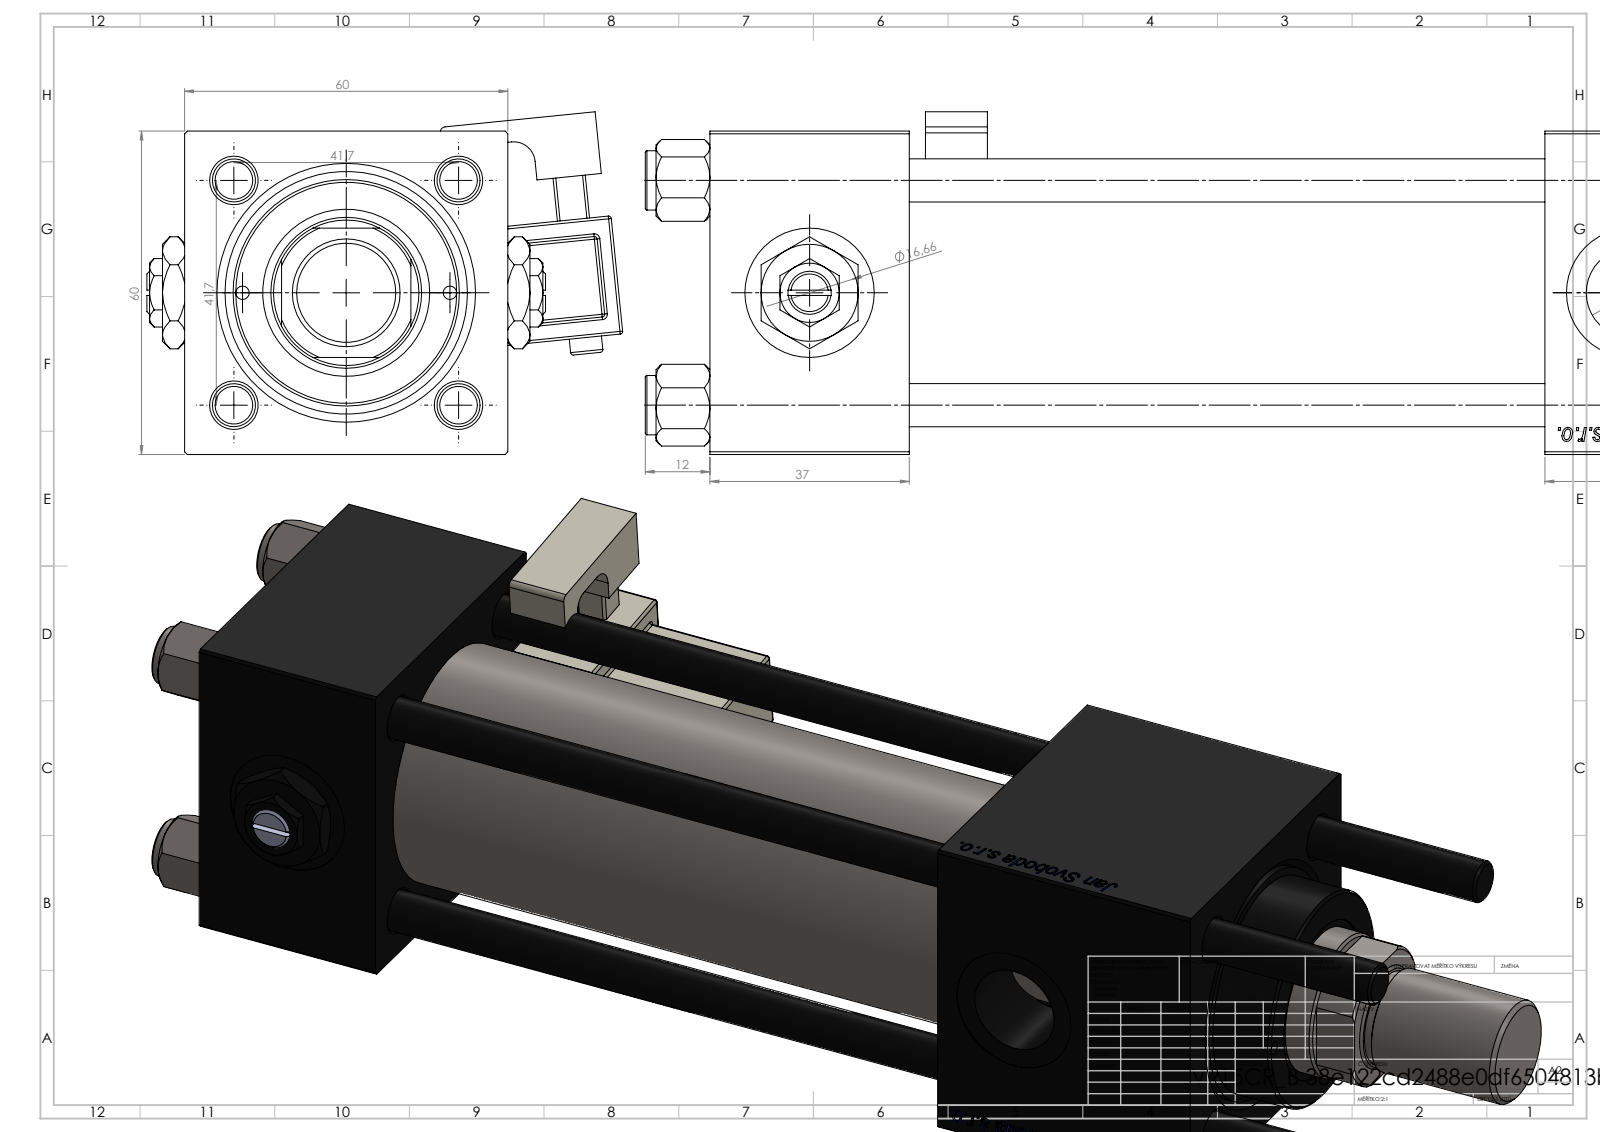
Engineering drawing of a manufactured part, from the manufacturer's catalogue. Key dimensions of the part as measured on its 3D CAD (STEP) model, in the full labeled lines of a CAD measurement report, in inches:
Part name (STEP PRODUCT): NUT_M5_B; V215CR_B-1; V215_VC_A; V215CR_MSU (+4 more)
STEP written by: SolidWorks 2019 (CONFIG_CONTROL_DESIGN)
Units: inches
Bodies: 15 solids, 1356 faces (516 planar, 126 cylindrical, 714 other)
Overall size (bounding box): 10.748 × 3.477 × 2.503
Volume: 32.62 in³ · Surface area: 246.5 in²
Round holes (diameter × count): ⌀0.315 ×4, ⌀0.098 ×2, ⌀0.276 ×2, ⌀0.656 ×2, ⌀0.945 ×2, ⌀0.728 ×1, ⌀1.102 ×1, ⌀1.22 ×1, ⌀1.575 ×1, ⌀1.772 ×1
Round bosses / shafts (diameter × count): ⌀0.433 ×4, ⌀1.811 ×1, ⌀1.654 ×1, ⌀0.787 ×1, ⌀0.709 ×1, ⌀0.236 ×1
Partial cylindrical surfaces — rounded edges, fillets, slot ends (radius × count): R0.02 ×24, R0.039 ×1, R0.098 ×1, R0.157 ×1, R0.531 ×1
Main face-to-face distances: 2.362, 1.457, 6.102, 4.646, 2.087, 7.059, 5.602, 0.957, 8.189, 6.732
Hole centre spacings: 0.823, 1.161, 1.642, 1.78, 0.758, 2.322, 1.516, 6.004
